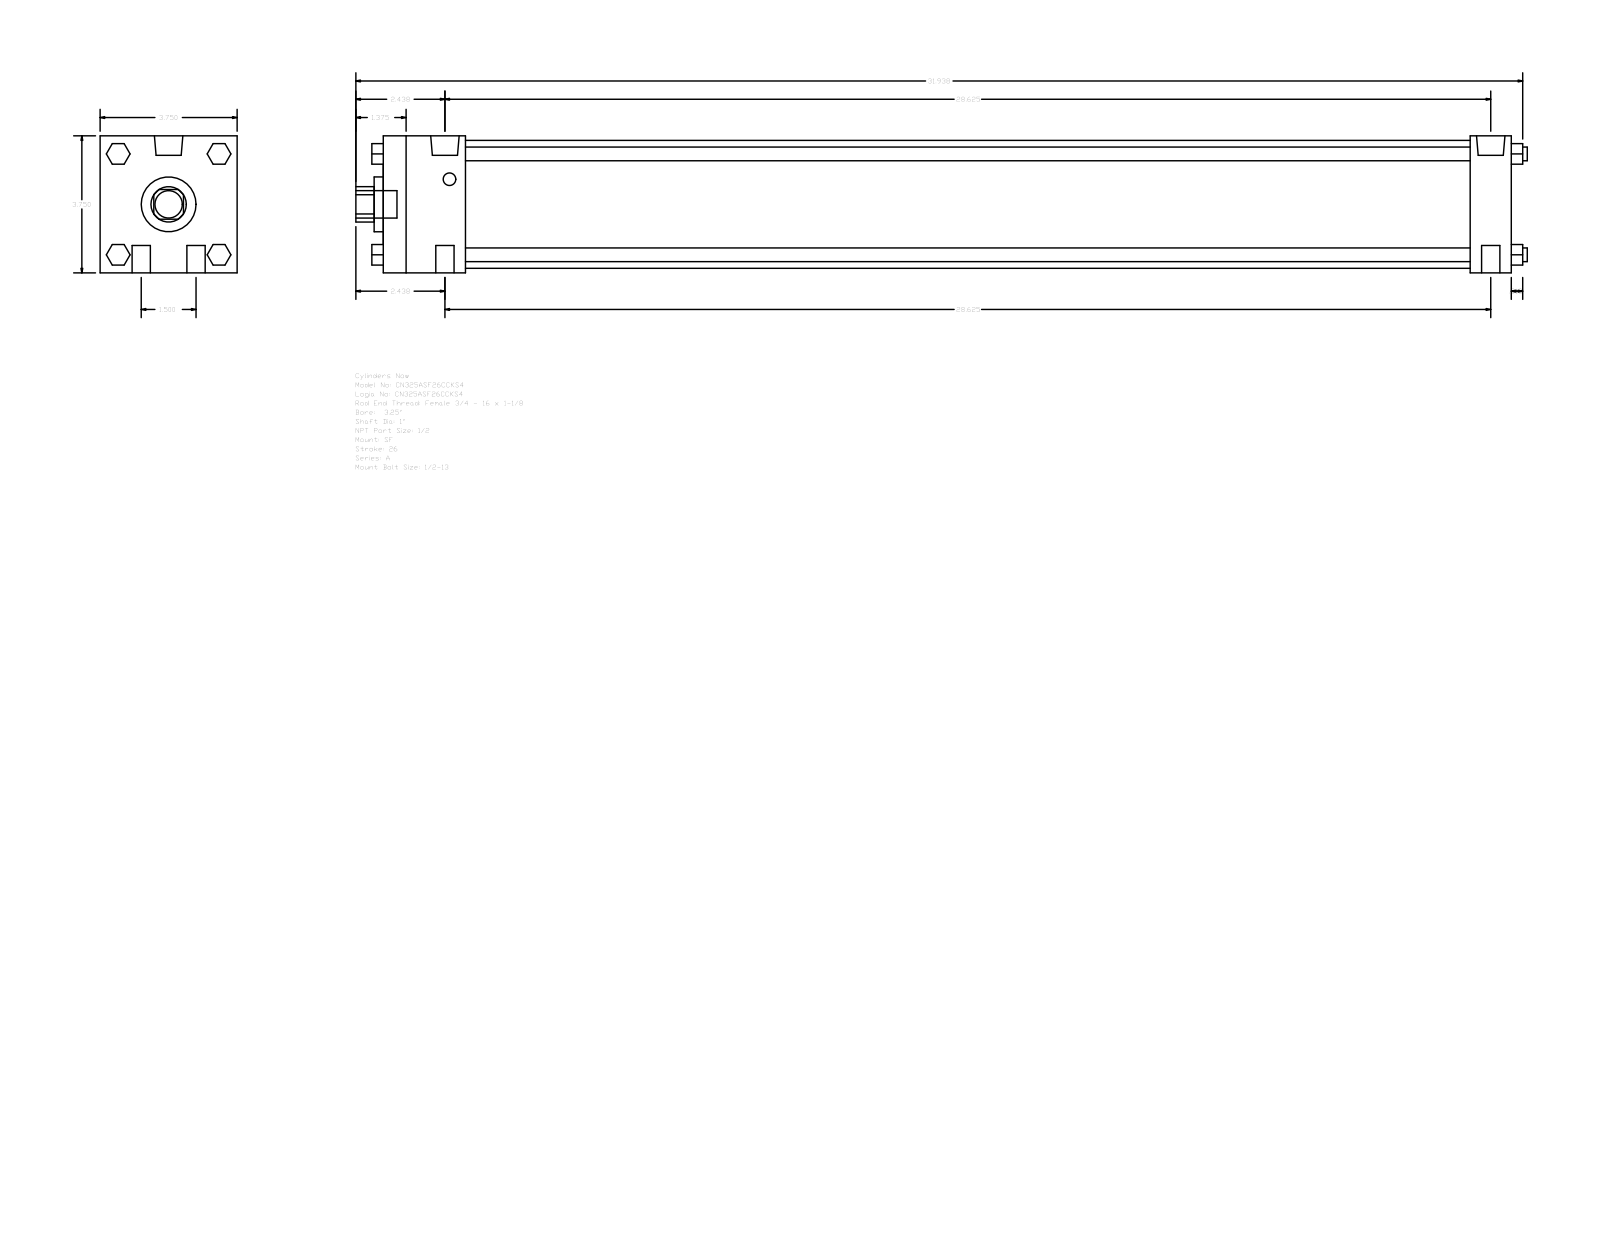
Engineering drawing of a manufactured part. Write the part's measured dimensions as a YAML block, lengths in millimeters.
part_name: "A_SF__0325_1"
step_written_by: "GSSL Pune (CONFIG_CONTROL_DESIGN)"
units: millimeters
bodies: {solids: 0, faces: 124, planar: 94, cylindrical: 30, other: 0}
overall_size: [814.39, 95.25, 95.25]
round_holes:
  - {diameter: 25.4, count: 1}
  - {diameter: 38.1, count: 1}
  - {diameter: 88.9, count: 1}
round_bosses_or_shafts:
  - {diameter: 12.7, count: 4}
  - {diameter: 9.53, count: 4}
  - {diameter: 19.77, count: 2}
  - {diameter: 8.73, count: 2}
  - {diameter: 19.05, count: 1}
partial_cylinders:
  - {radius: 12.29, count: 1}
face_to_face_distances: [95.24, 784.22, 28.57, 755.65, 57.15, 698.5, 727.07, 14.28, 35.05, 60.71]
